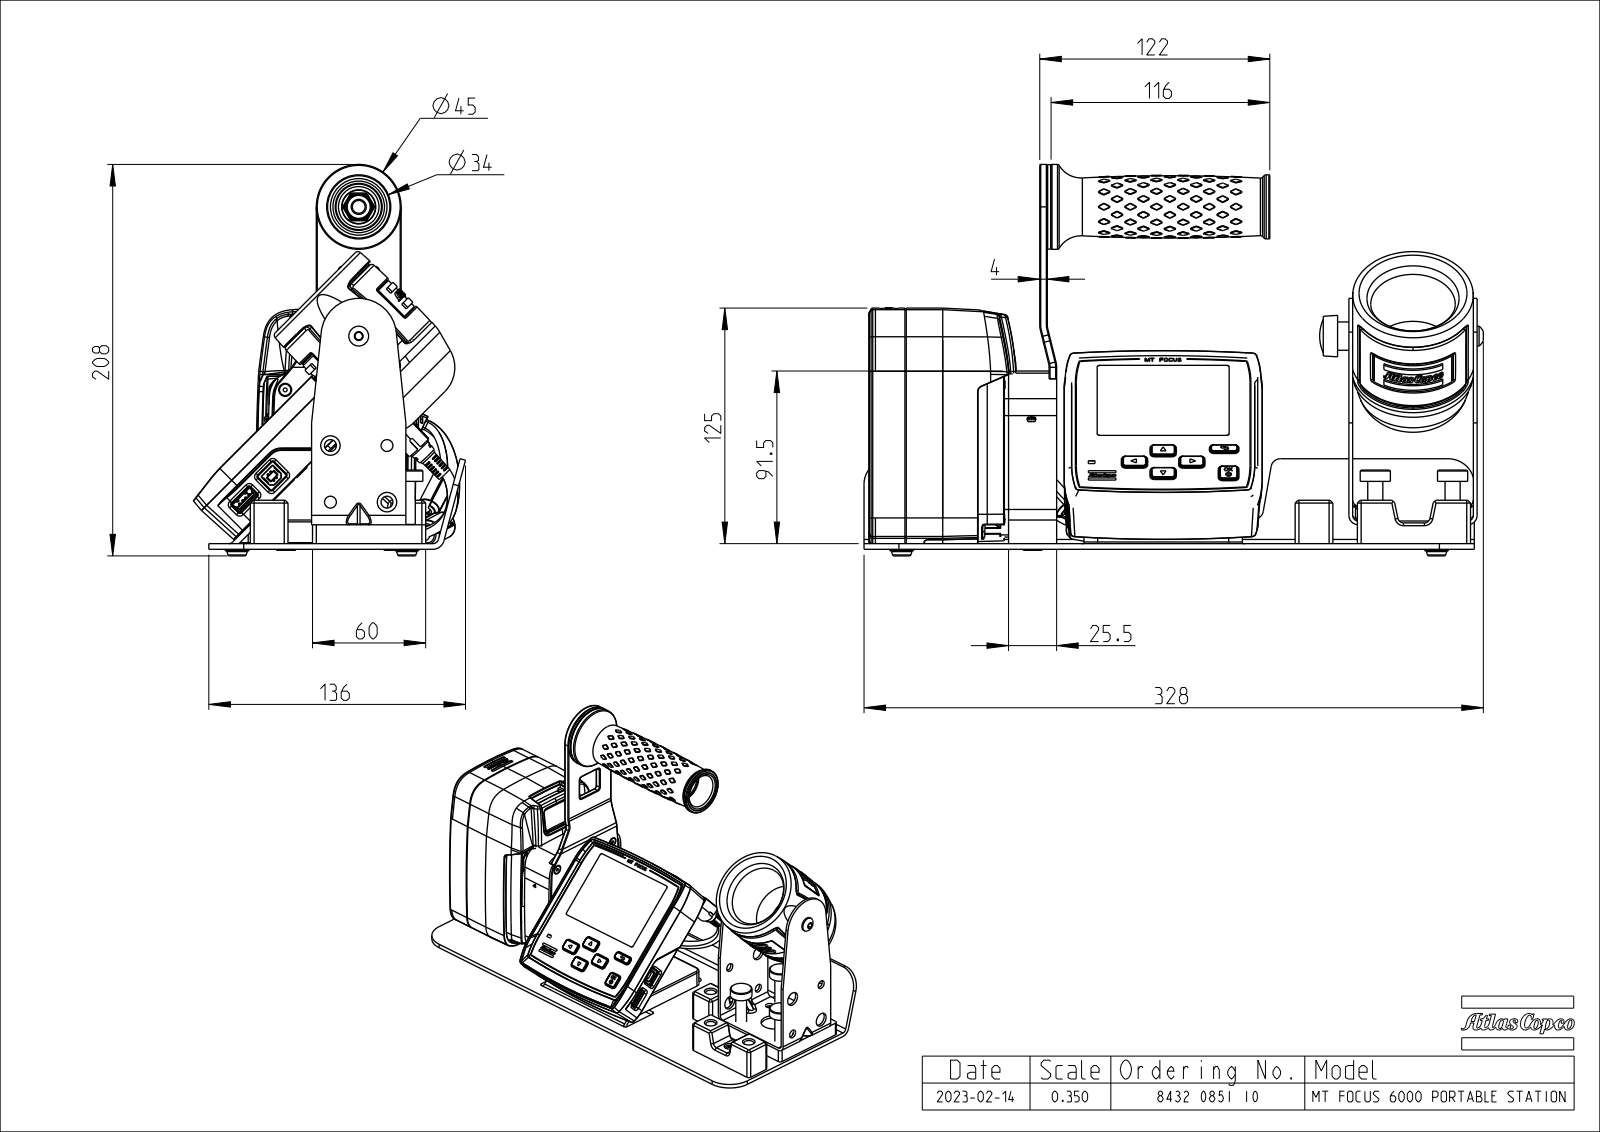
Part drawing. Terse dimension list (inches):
name: 4216425610_1; 4216425200_1; 4216425400_1; 4221000314_1 (+8 more)
written by: CREO PARAMETRIC BY PTC INC, 2020281 (CONFIG_CONTROL_DESIGN)
unit: in
bodies: 70 solids, 21947 faces (10618 planar, 3944 cylindrical, 7385 other)
size: 12.931 × 8.169 × 5.681
volume: 57.07 in³; area: 941.5 in²
holes: 18× ⌀0.126, 15× ⌀0.197, 12× ⌀0.248, 10× ⌀0.118, 10× ⌀0.13, 9× ⌀0.098, 8× ⌀0.106, 8× ⌀0.177, 7× ⌀0.081, 7× ⌀0.157, 6× ⌀0.163, 5× ⌀0.134
bosses: 8× ⌀0.157, 7× ⌀0.236, 6× ⌀0.051, 5× ⌀0.315, 5× ⌀0.118, 4× ⌀0.63, 4× ⌀0.5, 3× ⌀0.394
rounds: 807× R0.012, 486× R0.039, 309× R0.02, 266× R0.01, 110× R0.008, 80× R0.079, 74× R0.006, 54× R0.016
face distances: 0.118, 0.079, 0.157, 1.055, 12.563, 0.512, 1.134, 9.965, 0.937, 1.016
hole spacings: 0.669, 1.318, 0.458, 0.86, 1.025, 1.159, 1.258, 0.232
